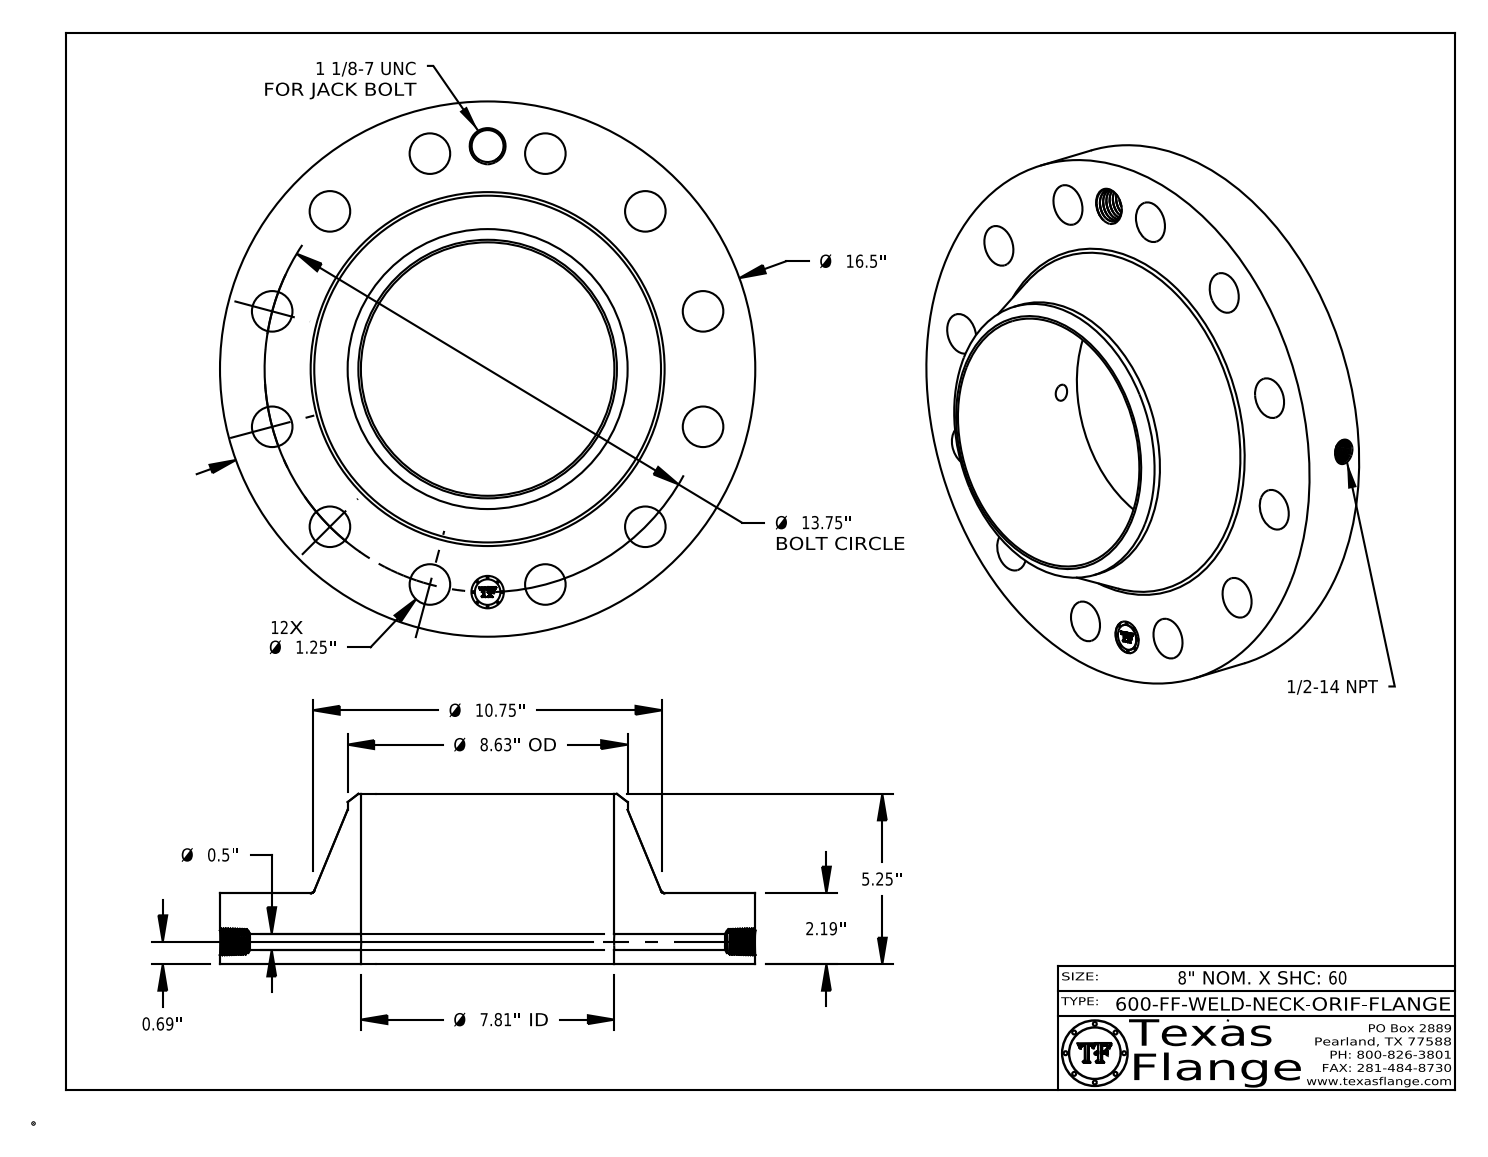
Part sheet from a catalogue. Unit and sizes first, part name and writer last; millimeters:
Units: millimetres
Overall size (bounding box): 419.1 × 419.1 × 133.4
Round holes (diameter × count): ⌀31.8 ×12, ⌀12.7 ×1, ⌀17.1 ×1, ⌀25 ×1, ⌀25.4 ×1, ⌀198.5 ×1
Round bosses / shafts (diameter × count): ⌀1.5 ×8, ⌀419.1 ×1, ⌀219.2 ×1, ⌀20 ×1
Main face-to-face distances: 55.6, 133.4, 77.7, 0.4, 55.2, 78.1, 7.6, 7.4, 1.4, 6.3
Hole centre spacings: 174.6, 302.5, 90.4, 174.6, 246.9, 337.3, 45.6, 90.4
Volume: 6 525 000 mm³ · Surface area: 473 400 mm²
Bodies: 1 solid, 777 faces (368 planar, 100 cylindrical, 309 other)
Part name (STEP PRODUCT): 600-FF-WELD-NECK
STEP written by: CATIA V5 STEP AP214 (AUTOMOTIVE_DESIGN)
